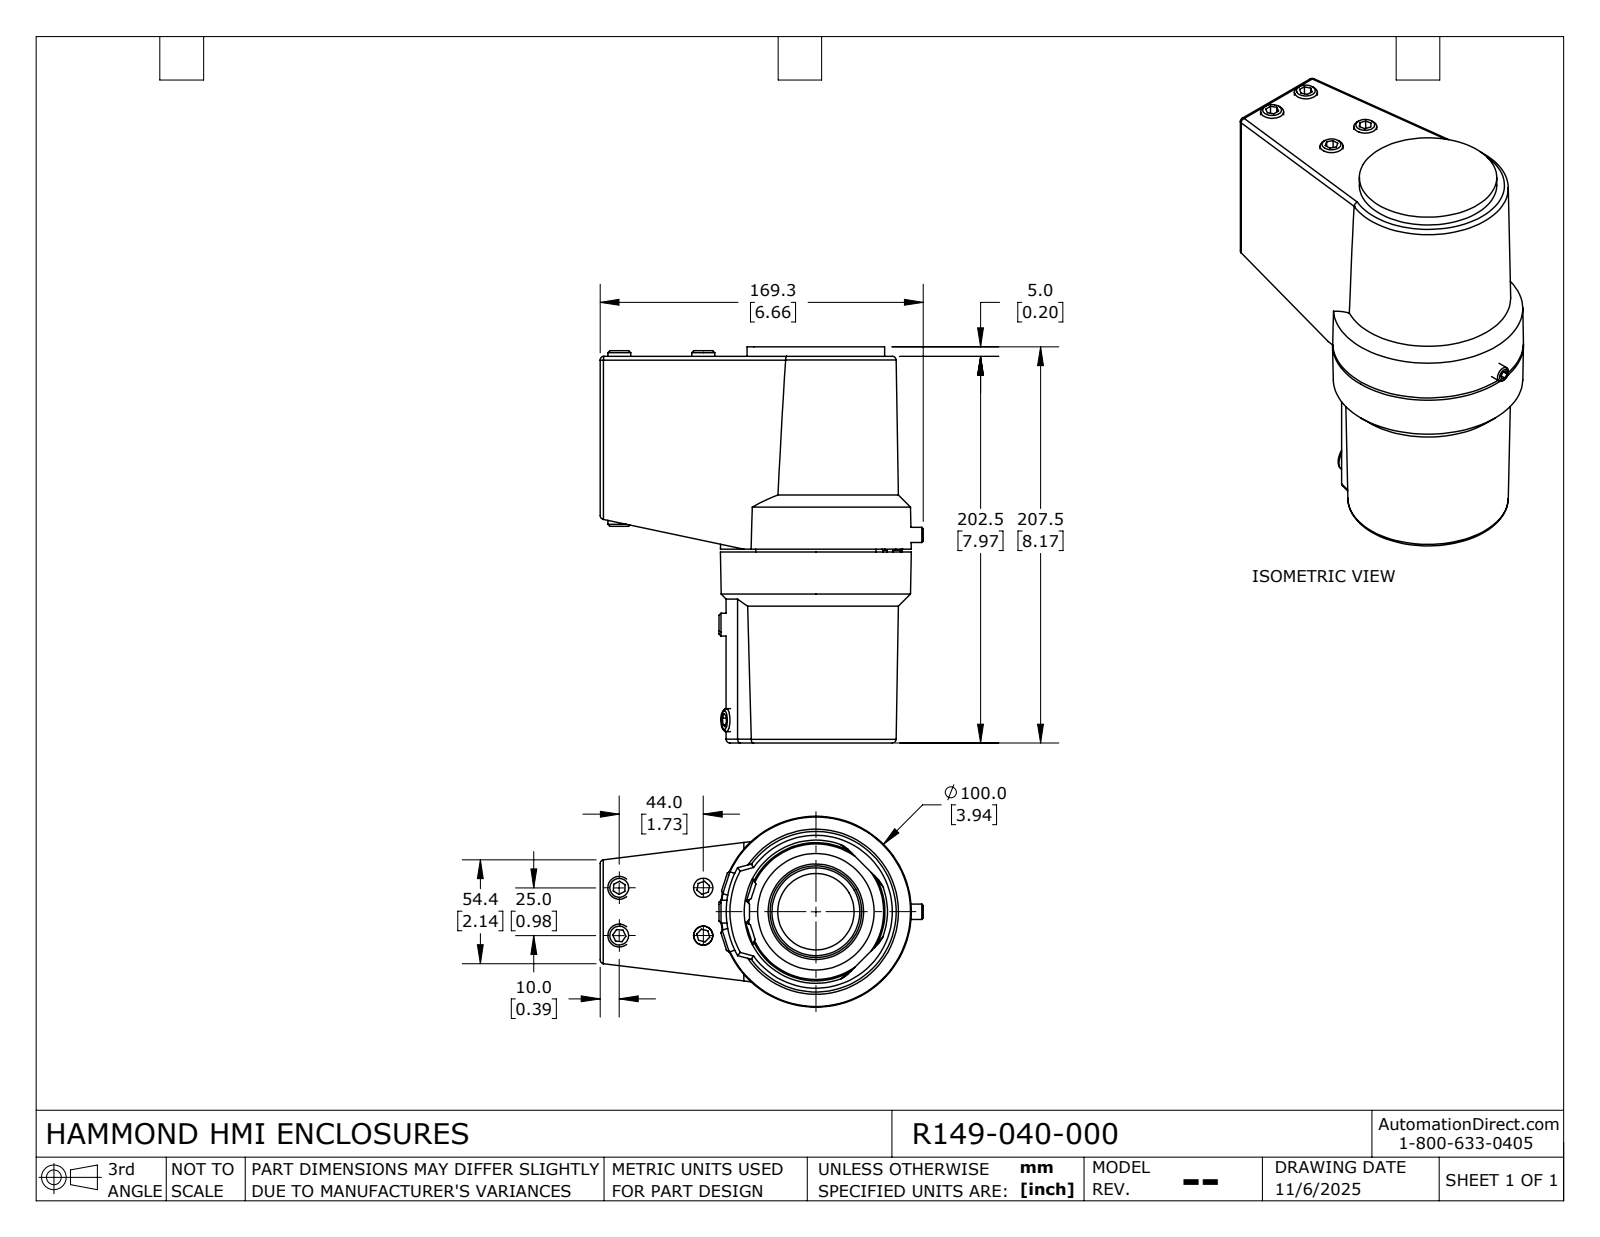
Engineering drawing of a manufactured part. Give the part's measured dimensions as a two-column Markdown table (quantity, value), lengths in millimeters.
| quantity | value |
| --- | --- |
| part name | R149-040-000 |
| STEP written by | SolidWorks 2024 (AUTOMOTIVE_DESIGN) |
| units | millimeters |
| bodies | 23 solids, 447 faces (228 planar, 96 cylindrical, 123 other) |
| overall size | 636.5 × 611.26 × 100 |
| volume | 1 321 000 mm³ |
| surface area | 623 630 mm² |
| round holes (diameter × count) | 10.11 × 3, 6.65 × 1, 40 × 1, 50.2 × 1, 50.5 × 1, 50.6 × 1, 61 × 1, 64 × 1, 65.3 × 1, 93 × 1 |
| round bosses / shafts (diameter × count) | 12 × 7, 72 × 1, 71 × 1, 70 × 1, 69 × 1, 66 × 1, 63 × 1, 50 × 1 |
| partial cylindrical surfaces (radius × count) | 2 × 16, 4 × 16, 3 × 8, 1 × 6, 7.4 × 4, 35.75 × 1, 45.05 × 1, 47 × 1 |
| main face-to-face distances | 3, 37, 57, 40, 34, 60, 54, 16.01, 73.01, 5 |
| hole center spacings | 47 |
